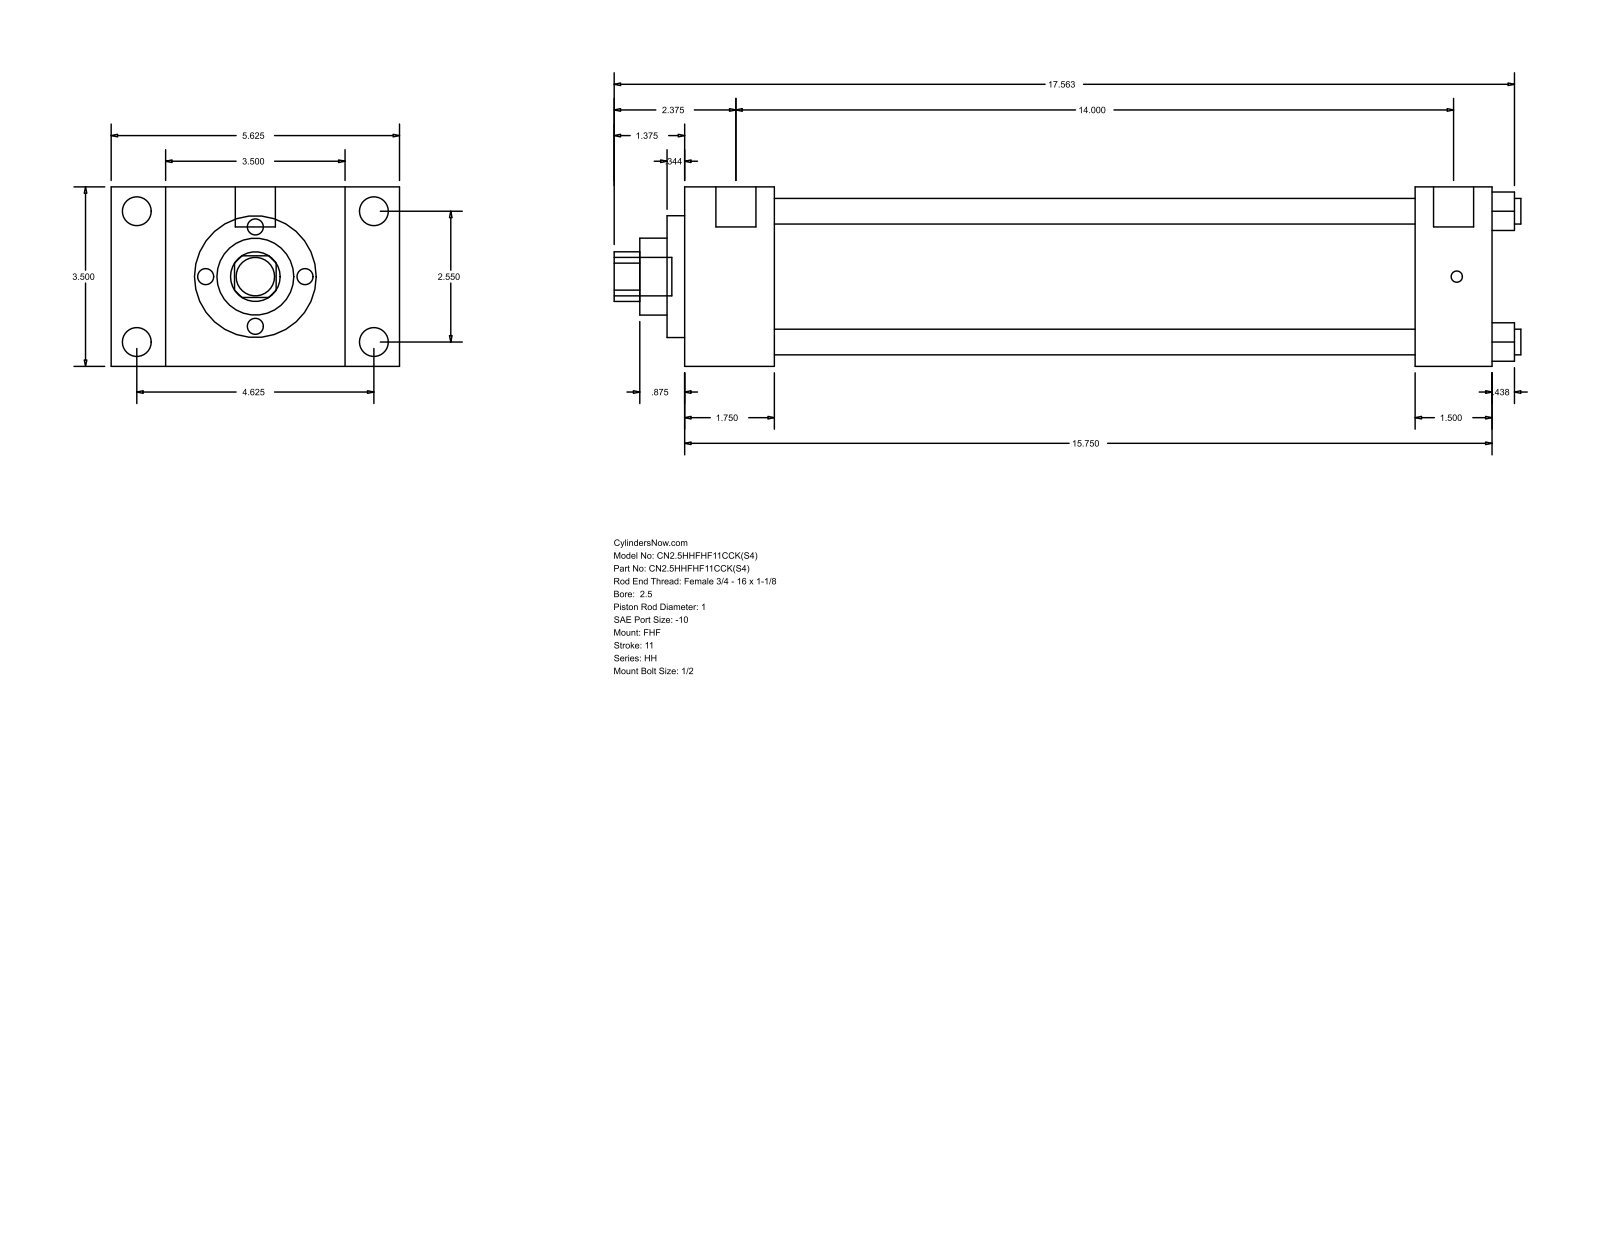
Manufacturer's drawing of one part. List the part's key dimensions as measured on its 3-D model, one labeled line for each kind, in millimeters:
Part name (STEP PRODUCT): HH_FHF__0250_1
STEP written by: GSSL Pune (CONFIG_CONTROL_DESIGN)
Units: millimetres
Bodies: 0 solids, 90 faces (61 planar, 29 cylindrical, 0 other)
Overall size (bounding box): 449.26 × 142.88 × 88.9
Round holes (diameter × count): ⌀12.7 ×4, ⌀25.4 ×1, ⌀38.1 ×1, ⌀60.33 ×1, ⌀73.03 ×1
Round bosses / shafts (diameter × count): ⌀14.3 ×4, ⌀5.56 ×4, ⌀19.84 ×2, ⌀19.05 ×1
Partial cylindrical surfaces — rounded edges, fillets, slot ends (radius × count): R12.29 ×1
Main face-to-face distances: 88.9, 44.46, 26.99, 115.89, 400.06, 355.6, 142.88, 361.96, 317.5, 38.1
Hole centre spacings: 45.79, 64.76, 91.58
